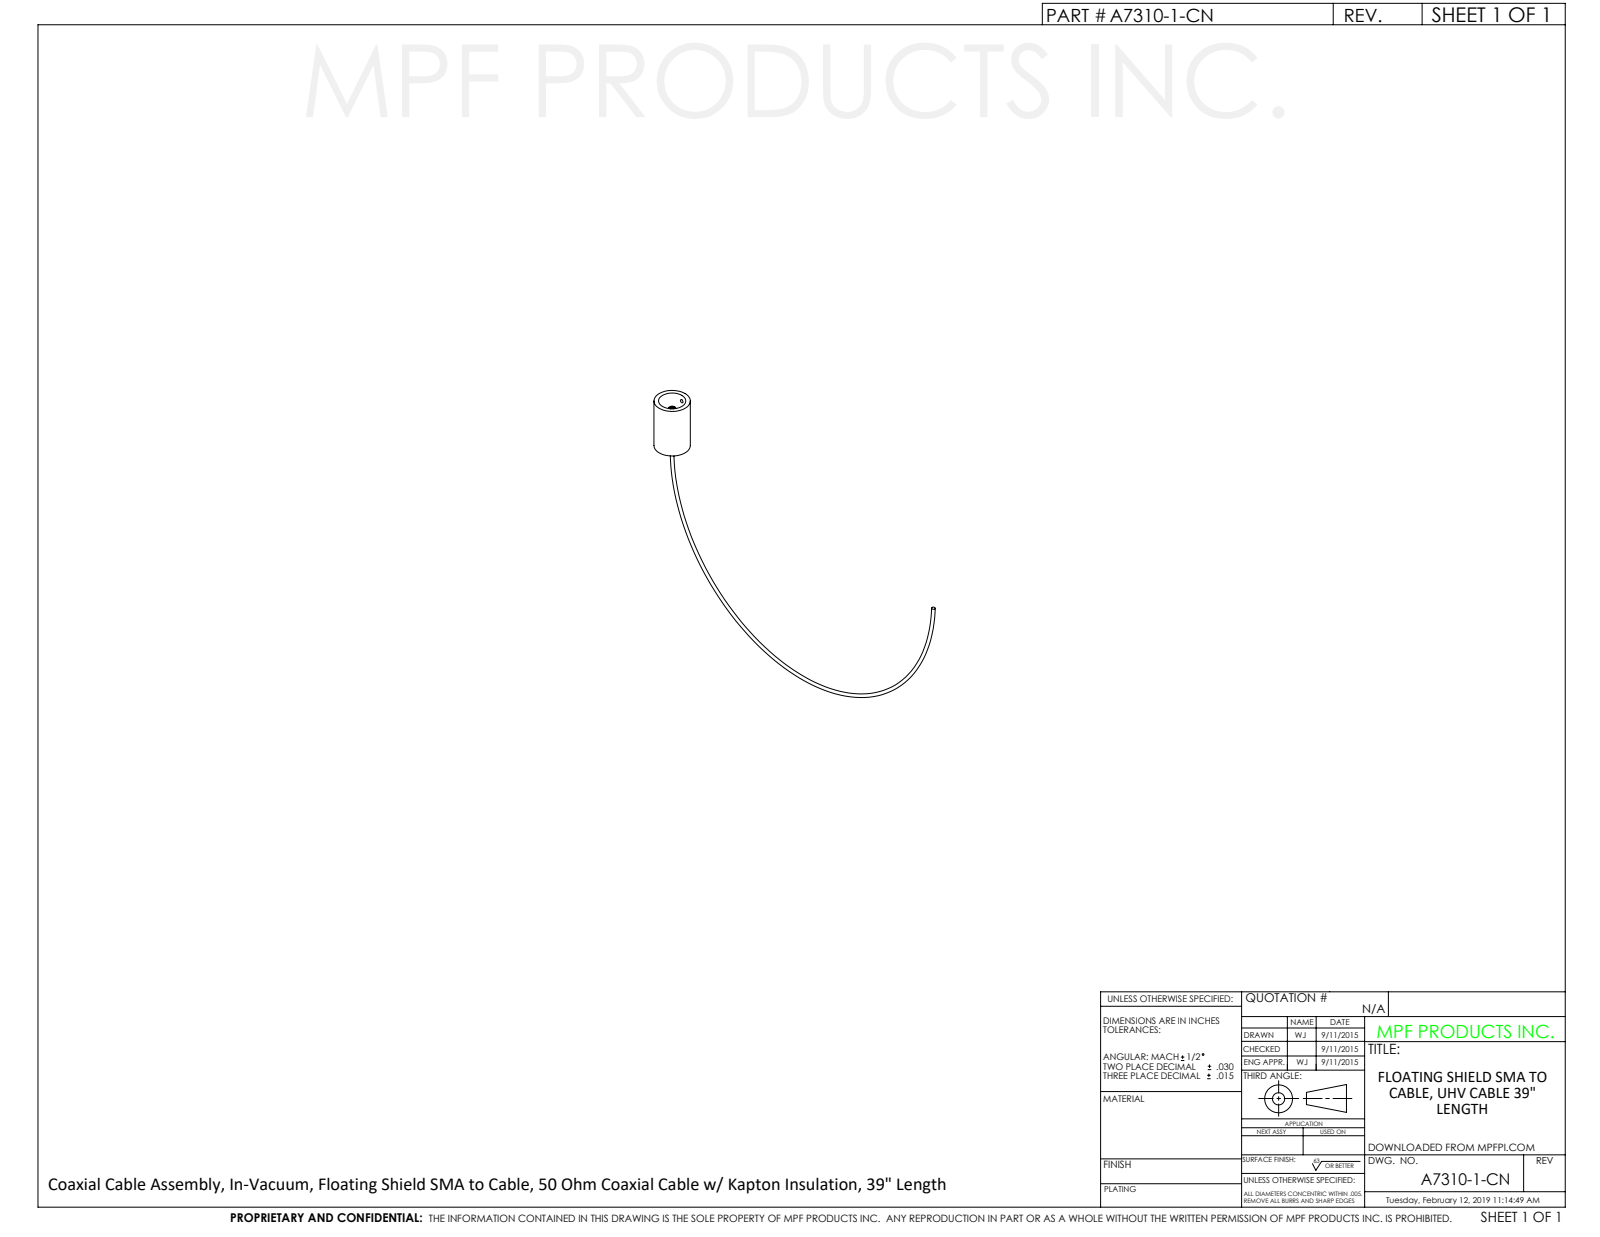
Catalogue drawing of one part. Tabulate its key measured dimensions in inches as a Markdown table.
| quantity | value |
| --- | --- |
| part name | A7309-1-CN |
| STEP written by | SolidWorks 2012 (CONFIG_CONTROL_DESIGN) |
| units | inches |
| bodies | 1 solid, 47 faces (22 planar, 20 cylindrical, 5 other) |
| overall size | 10.712 × 6.833 × 1 |
| volume | 0.992 in³ |
| surface area | 13.71 in² |
| round holes (diameter × count) | 0.1 × 3, 0.2 × 1, 0.75 × 1 |
| round bosses / shafts (diameter × count) | 1 × 1, 0.2 × 1 |
| main face-to-face distances | 1.5, 0.04, 0.02, 1.252, 0.248, 0.42, 0.38, 1.002, 0.25, 0.498 |
| hole center spacings | 0.35 |
